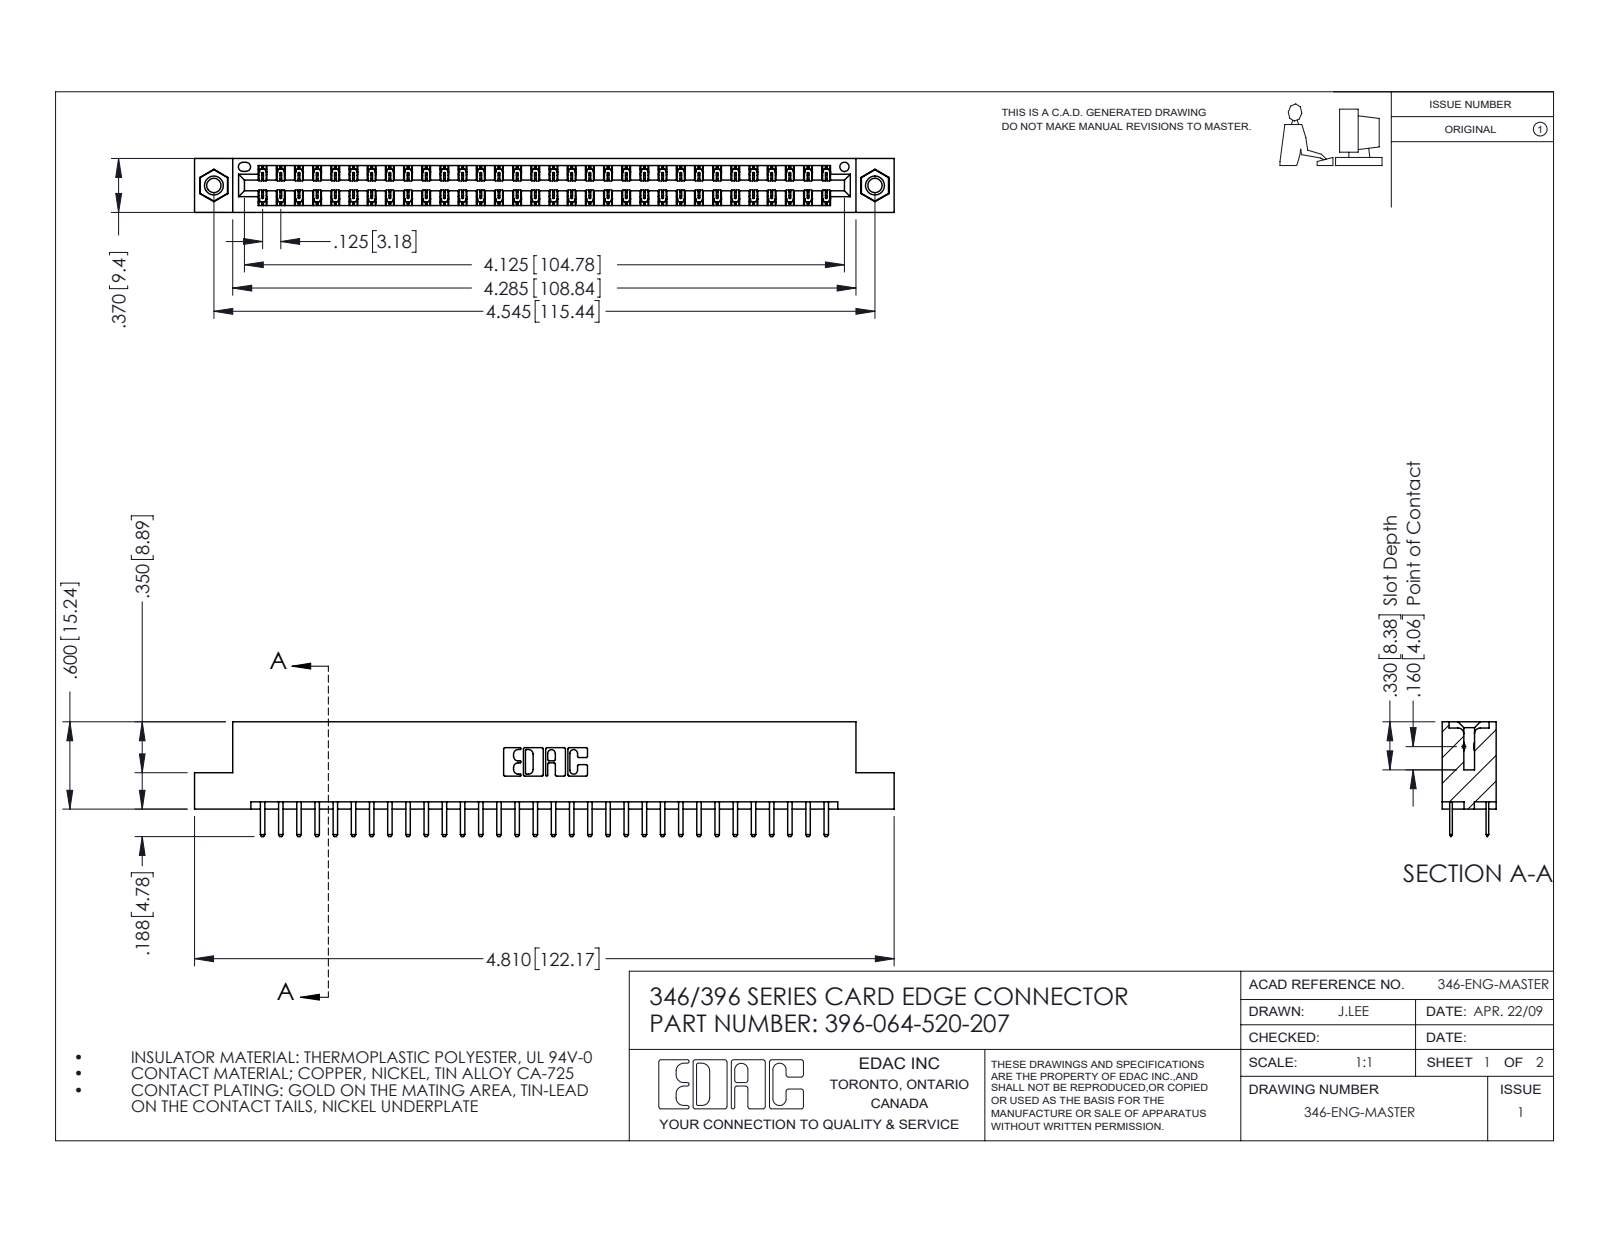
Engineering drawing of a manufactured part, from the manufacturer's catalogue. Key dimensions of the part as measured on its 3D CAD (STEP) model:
Part name (STEP PRODUCT): 345-292-001_345-293-120; 396-064-520-207; 345-250-001_345-250-005-103; 346 Part_Flush Mounting Lugs - 0.156 Dia-TI
STEP written by: SolidWorks 2016 (CONFIG_CONTROL_DESIGN)
Units: inches
Bodies: 67 solids, 3766 faces (2476 planar, 1274 cylindrical, 16 other)
Overall size (bounding box): 4.81 × 0.788 × 0.37
Volume: 0.72 in³ · Surface area: 24.83 in²
Round holes (diameter × count): ⌀0.098 ×2, ⌀0.125 ×2, ⌀0.156 ×2, ⌀0.064 ×1
Round bosses / shafts (diameter × count): ⌀0.155 ×2
Partial cylindrical surfaces — rounded edges, fillets, slot ends (radius × count): R0.006 ×96, R0.01 ×68, R0.01 ×22, R0.007 ×6, R0.031 ×6, R0.026 ×3, R0.014 ×2, R0.022 ×2
Main face-to-face distances: 0.048, 0.322, 0.25, 0.37, 0.275, 0.072, 0.298, 0.025, 0.148, 0.222
Hole centre spacings: 0.246, 4.337, 4.545
